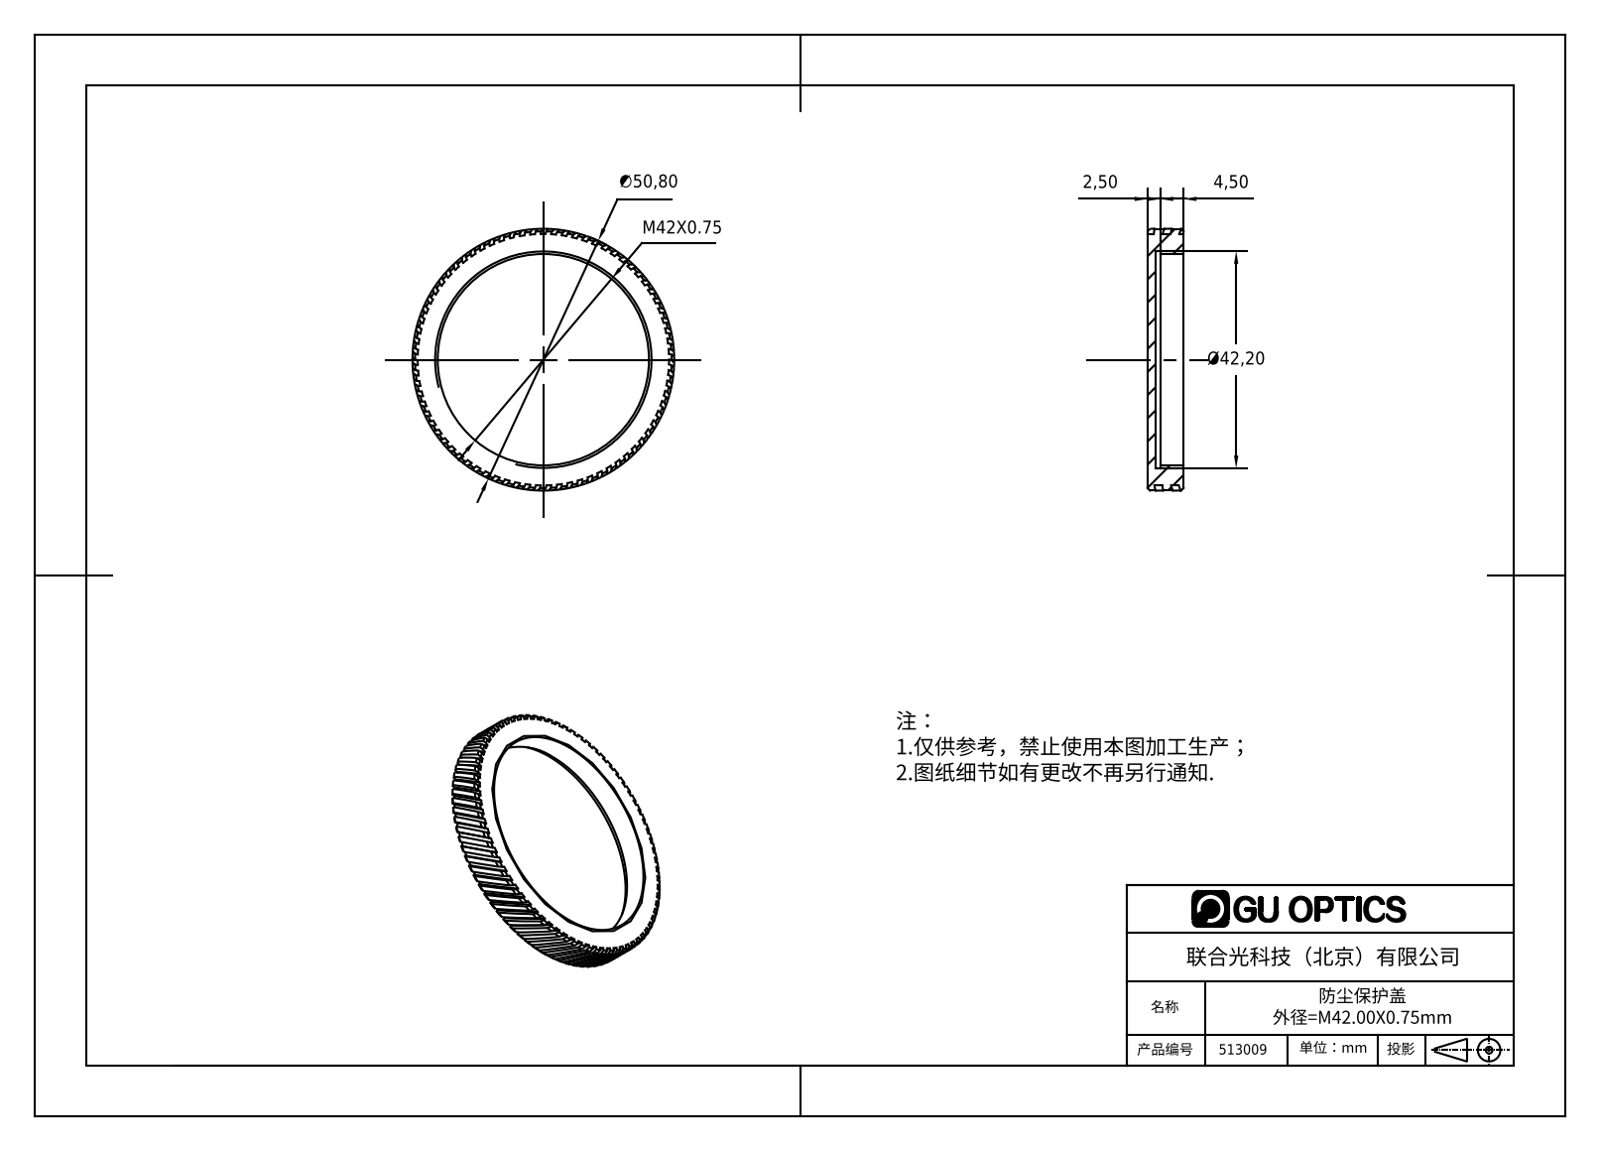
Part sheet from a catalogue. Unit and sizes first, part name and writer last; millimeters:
Units: millimetres
Overall size (bounding box): 50.8 × 50.8 × 7
Round holes (diameter × count): ⌀41 ×1, ⌀42.2 ×1
Round bosses / shafts (diameter × count): ⌀50.8 ×1, ⌀48.8 ×1
Main face-to-face distances: 1.5, 5.5, 7, 0.8, 4.5, 1, 2.5, 0.81, 0.79
Volume: 6 324 mm³ · Surface area: 7 055 mm²
Bodies: 1 solid, 462 faces (154 planar, 156 cylindrical, 152 other)
Part name (STEP PRODUCT): 513009
STEP written by: SolidWorks 2016 (AUTOMOTIVE_DESIGN)
